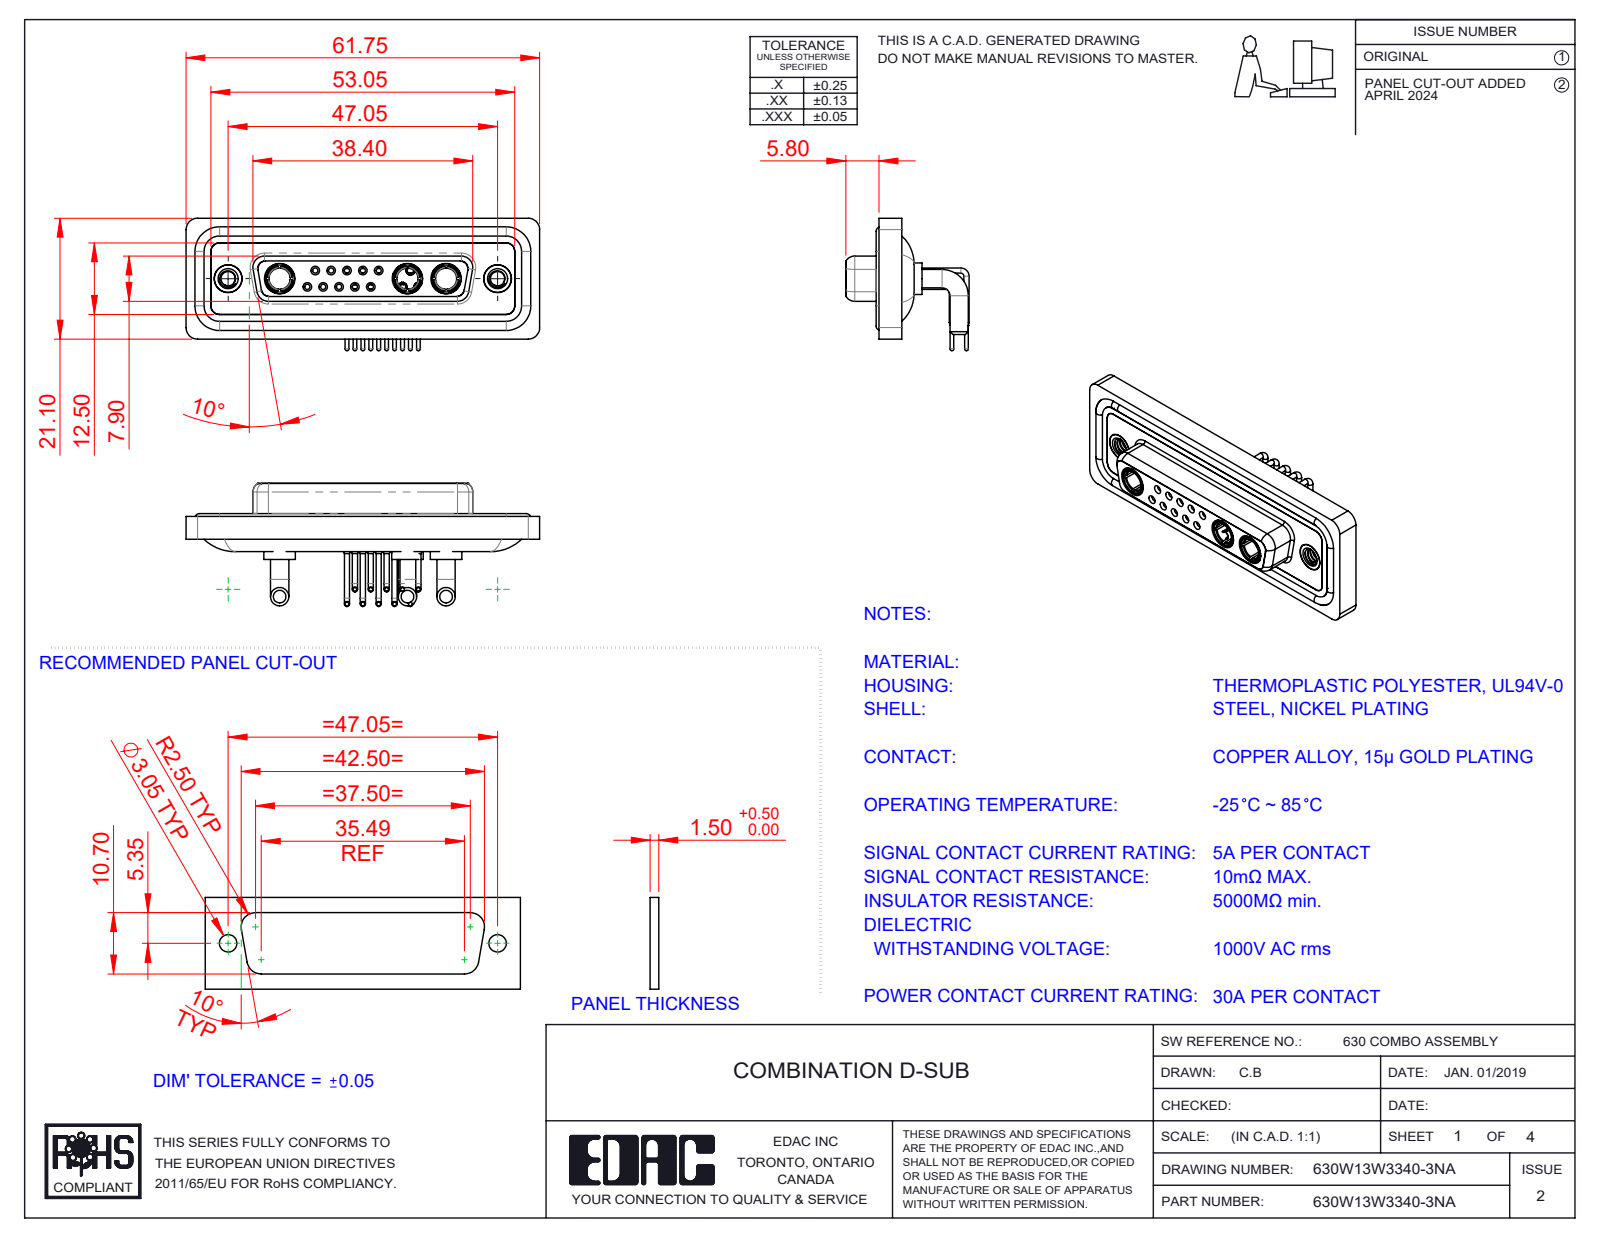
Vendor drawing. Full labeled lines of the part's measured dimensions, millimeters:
Part name (STEP PRODUCT): 630Combo Shell Rear_25 Contacts; 630Combo Housing_13W3; 630Combo Threaded Rivet_A; 630Combo Shell Front_25 Contacts (+5 more)
STEP written by: SolidWorks 2023 (CONFIG_CONTROL_DESIGN)
Units: millimetres
Bodies: 23 solids, 1144 faces (342 planar, 491 cylindrical, 311 other)
Overall size (bounding box): 61.75 × 23.12 × 21.53
Volume: 8 547 mm³ · Surface area: 14 355 mm²
Round holes (diameter × count): ⌀0.9 ×10, ⌀1.1 ×10, ⌀1.5 ×10, ⌀2 ×10, ⌀1.6 ×5, ⌀1.7 ×5, ⌀4.85 ×5, ⌀3.7 ×3, ⌀5.3 ×3, ⌀2.5 ×2, ⌀4 ×2, ⌀4.05 ×2
Round bosses / shafts (diameter × count): ⌀0.9 ×15, ⌀1.6 ×12, ⌀0.65 ×10, ⌀3.2 ×6, ⌀2 ×5, ⌀1.5 ×5, ⌀5.5 ×3, ⌀5.2 ×3
Partial cylindrical surfaces — rounded edges, fillets, slot ends (radius × count): R1.5 ×18, R2 ×18, R1.35 ×8, R1.6 ×8, R0.25 ×4, R0.5 ×4, R0.6 ×4, R0.65 ×4
Main face-to-face distances: 0.4, 1.8, 4.1, 1.1, 1.6, 3.1, 1.5, 2.5, 3.7, 1.4
Hole centre spacings: 3.16, 2.77, 5.54, 5.04, 8.31, 5.03, 7.49, 11.08
